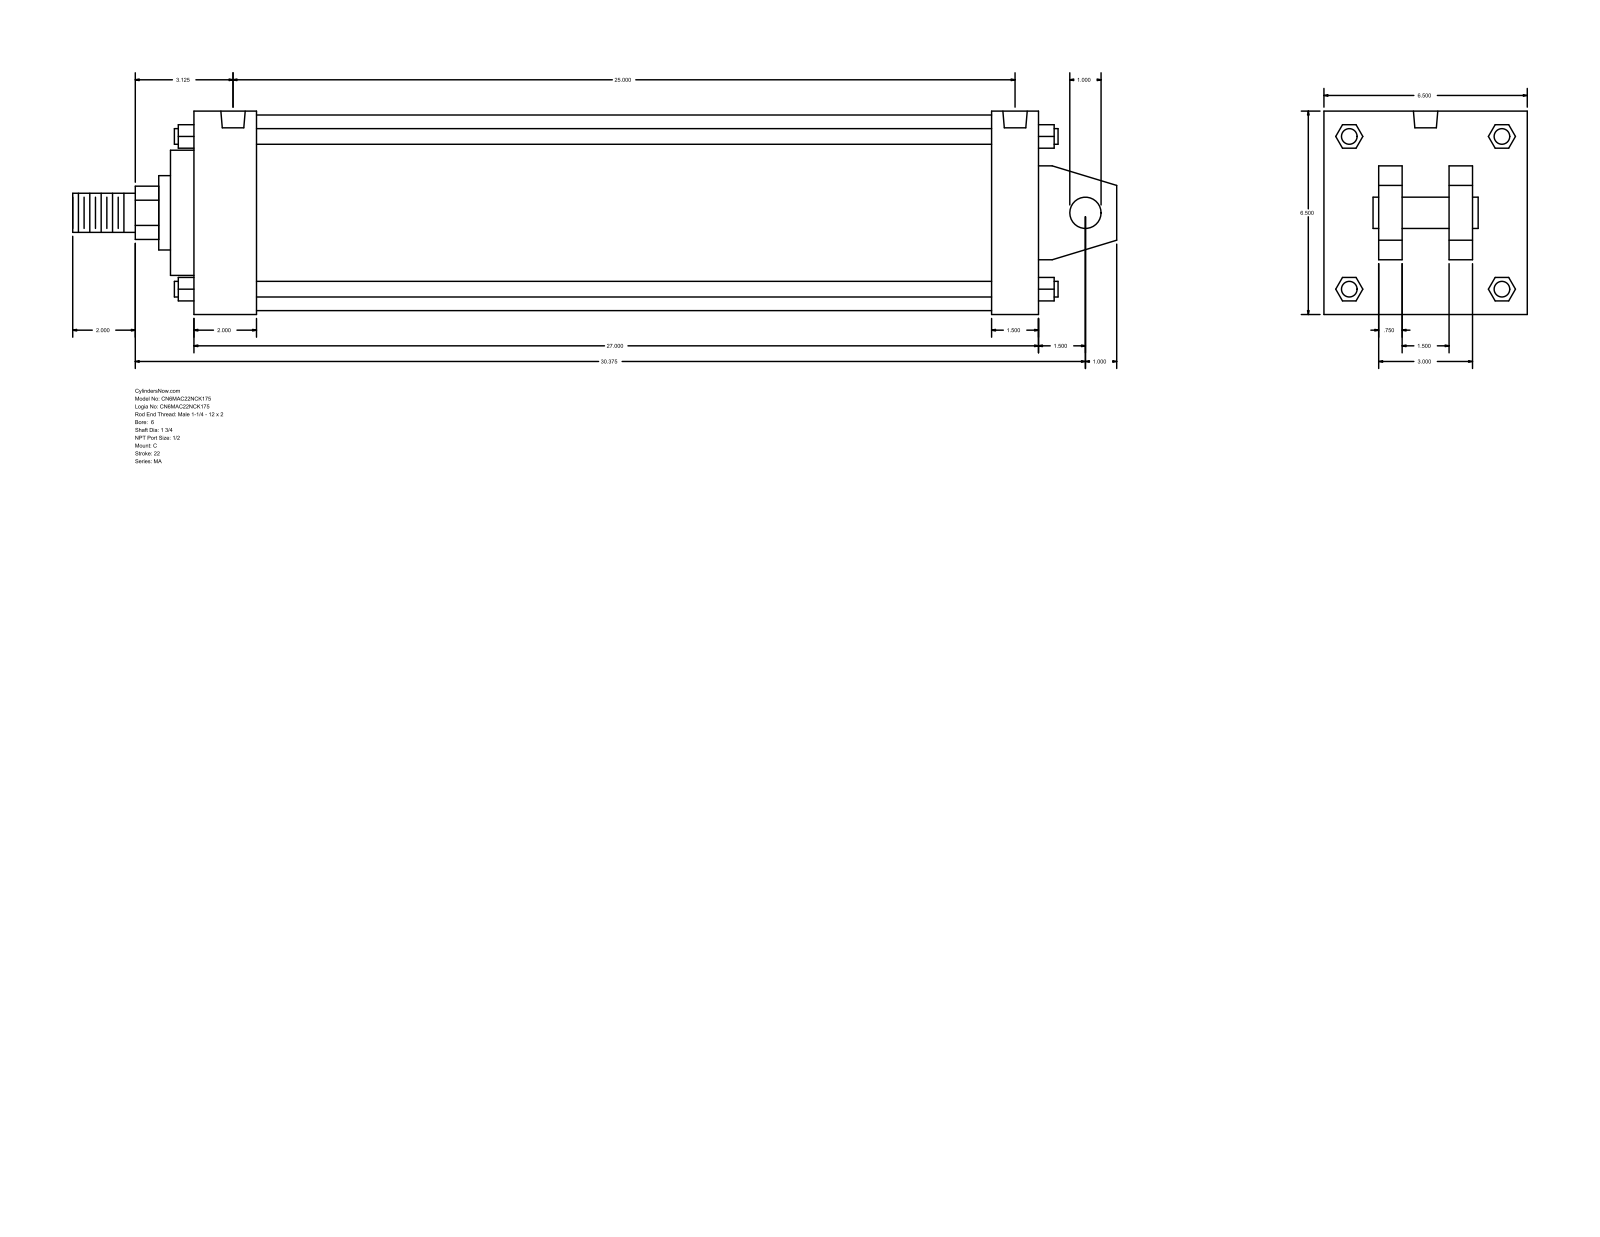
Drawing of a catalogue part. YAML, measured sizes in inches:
part_name: "MA_C__0600_1.75"
step_written_by: "GSSL Pune (CONFIG_CONTROL_DESIGN)"
units: inches
bodies: {solids: 0, faces: 141, planar: 109, cylindrical: 32, other: 0}
overall_size: [33.375, 6.5, 6.5]
round_holes:
  - {diameter: 0.687, count: 4}
  - {diameter: 0.778, count: 2}
round_bosses_or_shafts:
  - {diameter: 0.5, count: 4}
  - {diameter: 6.25, count: 1}
  - {diameter: 4, count: 1}
  - {diameter: 2.375, count: 1}
  - {diameter: 1.75, count: 1}
  - {diameter: 1.25, count: 1}
  - {diameter: 1, count: 1}
partial_cylinders:
  - {radius: 0.852, count: 1}
face_to_face_distances: [6.5, 27, 0.75, 2.5, 4, 2, 1.75, 4.75, 2.25, 25]
hole_center_spacings: [25]
